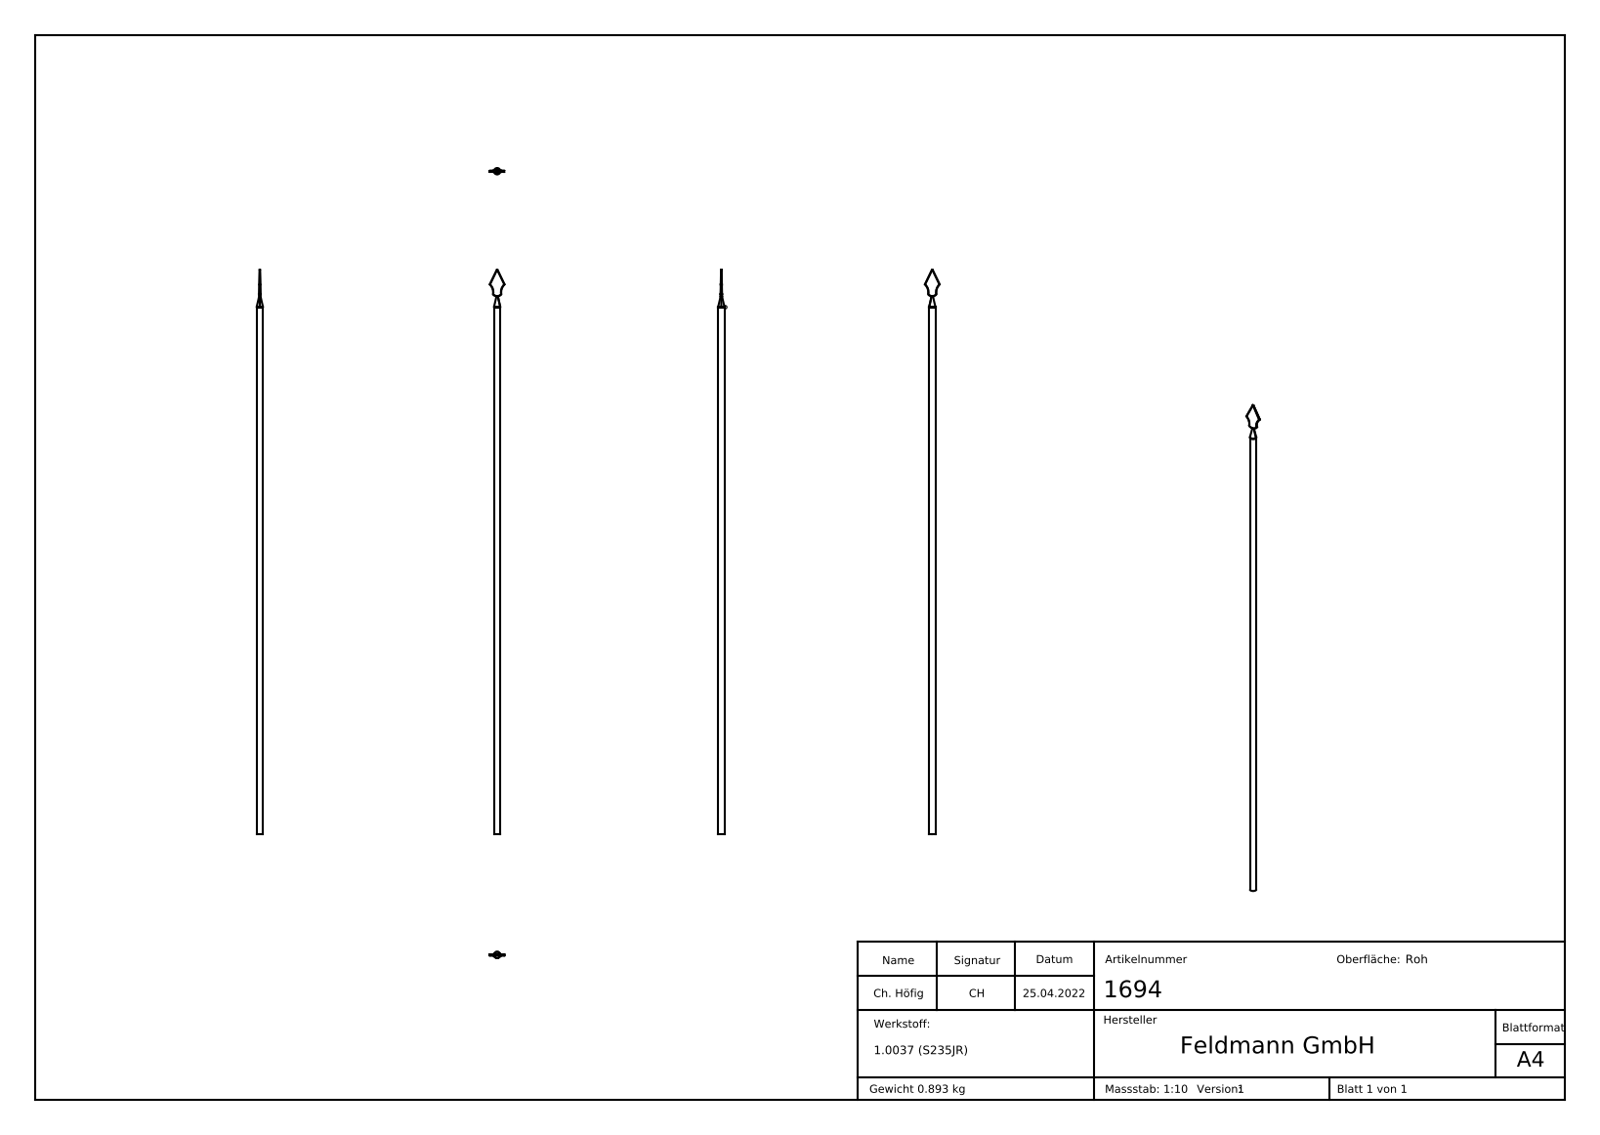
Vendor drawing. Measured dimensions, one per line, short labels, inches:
name: 1694
written by: SolidWorks 2018 (CONFIG_CONTROL_DESIGN)
unit: in
bodies: 1 solid, 252 faces (125 planar, 16 cylindrical, 111 other)
size: 41.732 × 1.085 × 0.472
volume: 6.99 in³; area: 61.49 in²
bosses: 1× ⌀0.472, 1× ⌀0.118
rounds: 5× R0.039, 4× R0.02, 2× R0.748, 1× R0.394
face distances: 0.087, 0.018, 0.022, 0.027, 0.013, 0.085, 0.093, 0.103, 0.064, 0.02
